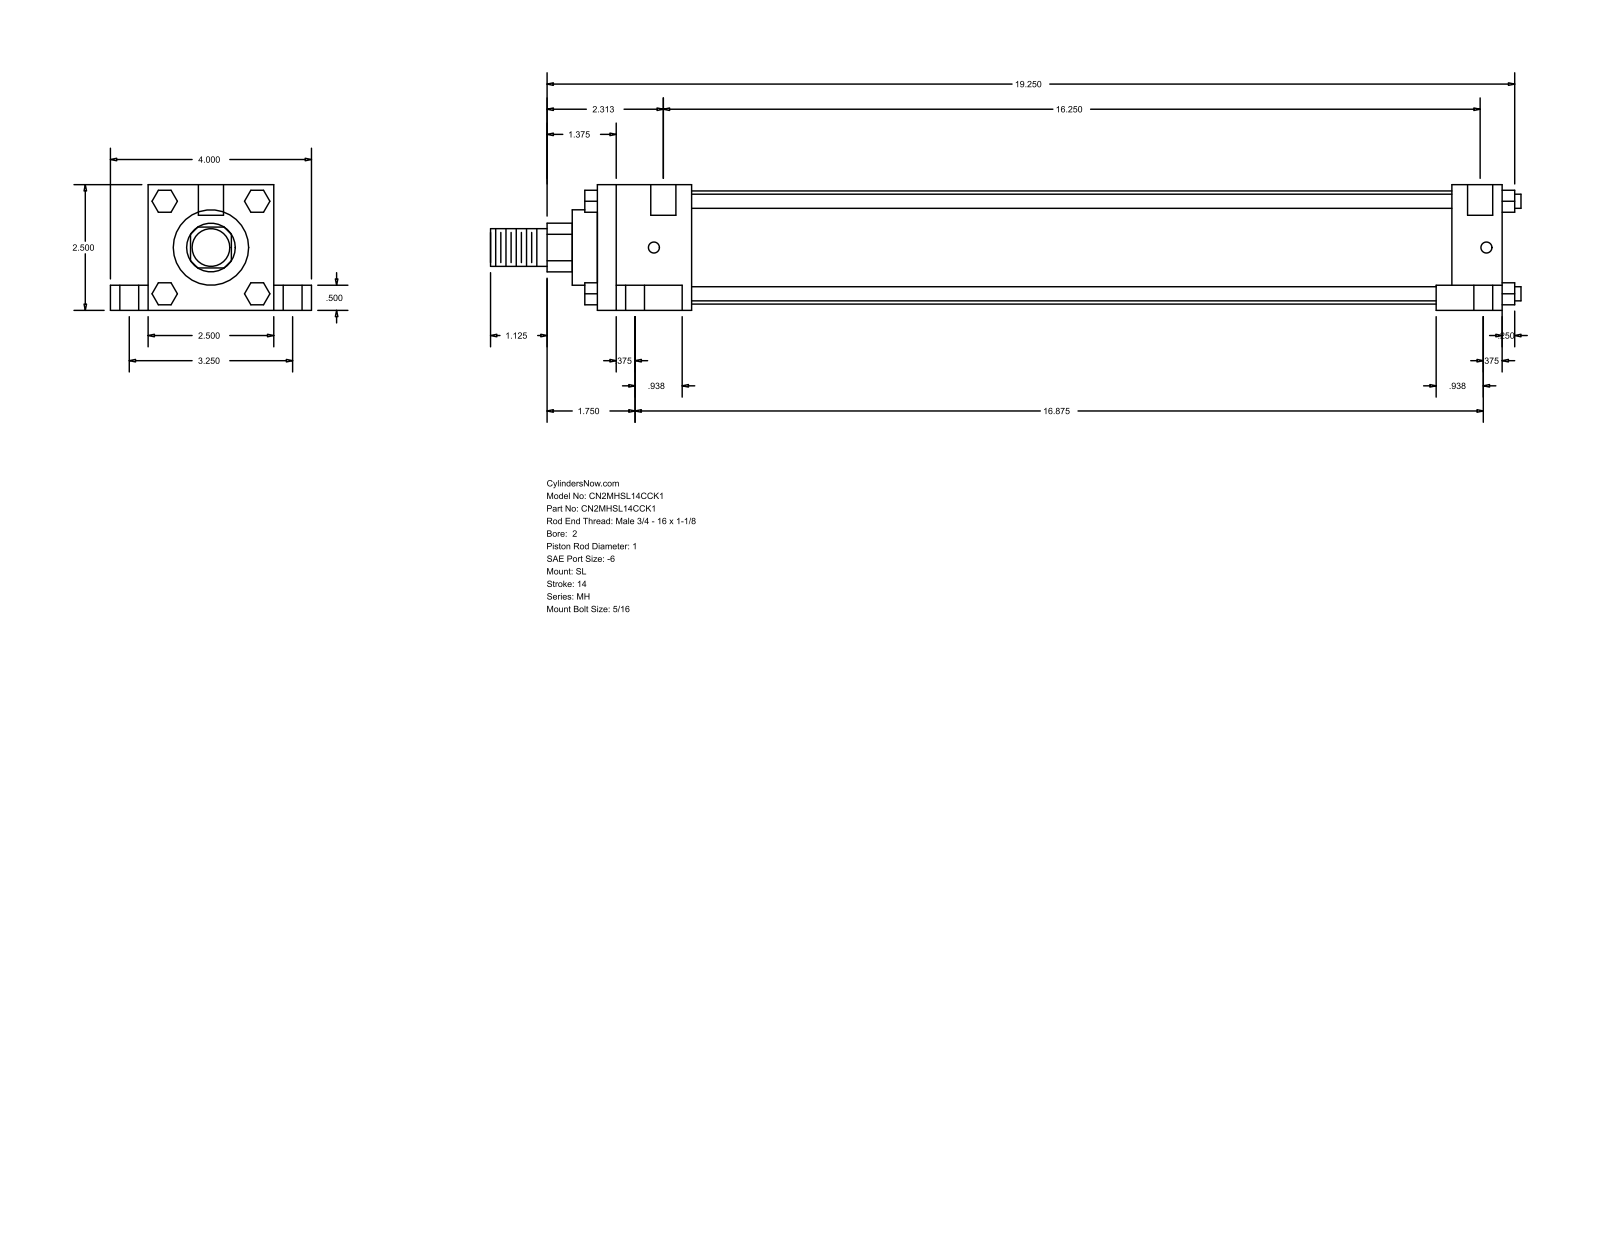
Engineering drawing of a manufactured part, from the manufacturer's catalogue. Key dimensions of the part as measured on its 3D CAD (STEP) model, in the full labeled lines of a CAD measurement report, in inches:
Part name (STEP PRODUCT): MH_SL__0200_1
STEP written by: GSSL Pune (CONFIG_CONTROL_DESIGN)
Units: inches
Bodies: 0 solids, 148 faces (112 planar, 36 cylindrical, 0 other)
Overall size (bounding box): 20.5 × 4 × 2.5
Round holes (diameter × count): ⌀0.219 ×4, ⌀0.375 ×4, ⌀0.625 ×4, ⌀0.5 ×2
Round bosses / shafts (diameter × count): ⌀0.281 ×4, ⌀2.25 ×1, ⌀1.5 ×1, ⌀1 ×1, ⌀0.75 ×1
Partial cylindrical surfaces — rounded edges, fillets, slot ends (radius × count): R0.484 ×1
Main face-to-face distances: 2.5, 18, 0.5, 0.75, 2, 3.25, 1, 17, 1.875, 15.125
Hole centre spacings: 1.626, 1.668, 1.719, 3.25, 16.393, 16.562, 16.58, 16.875
